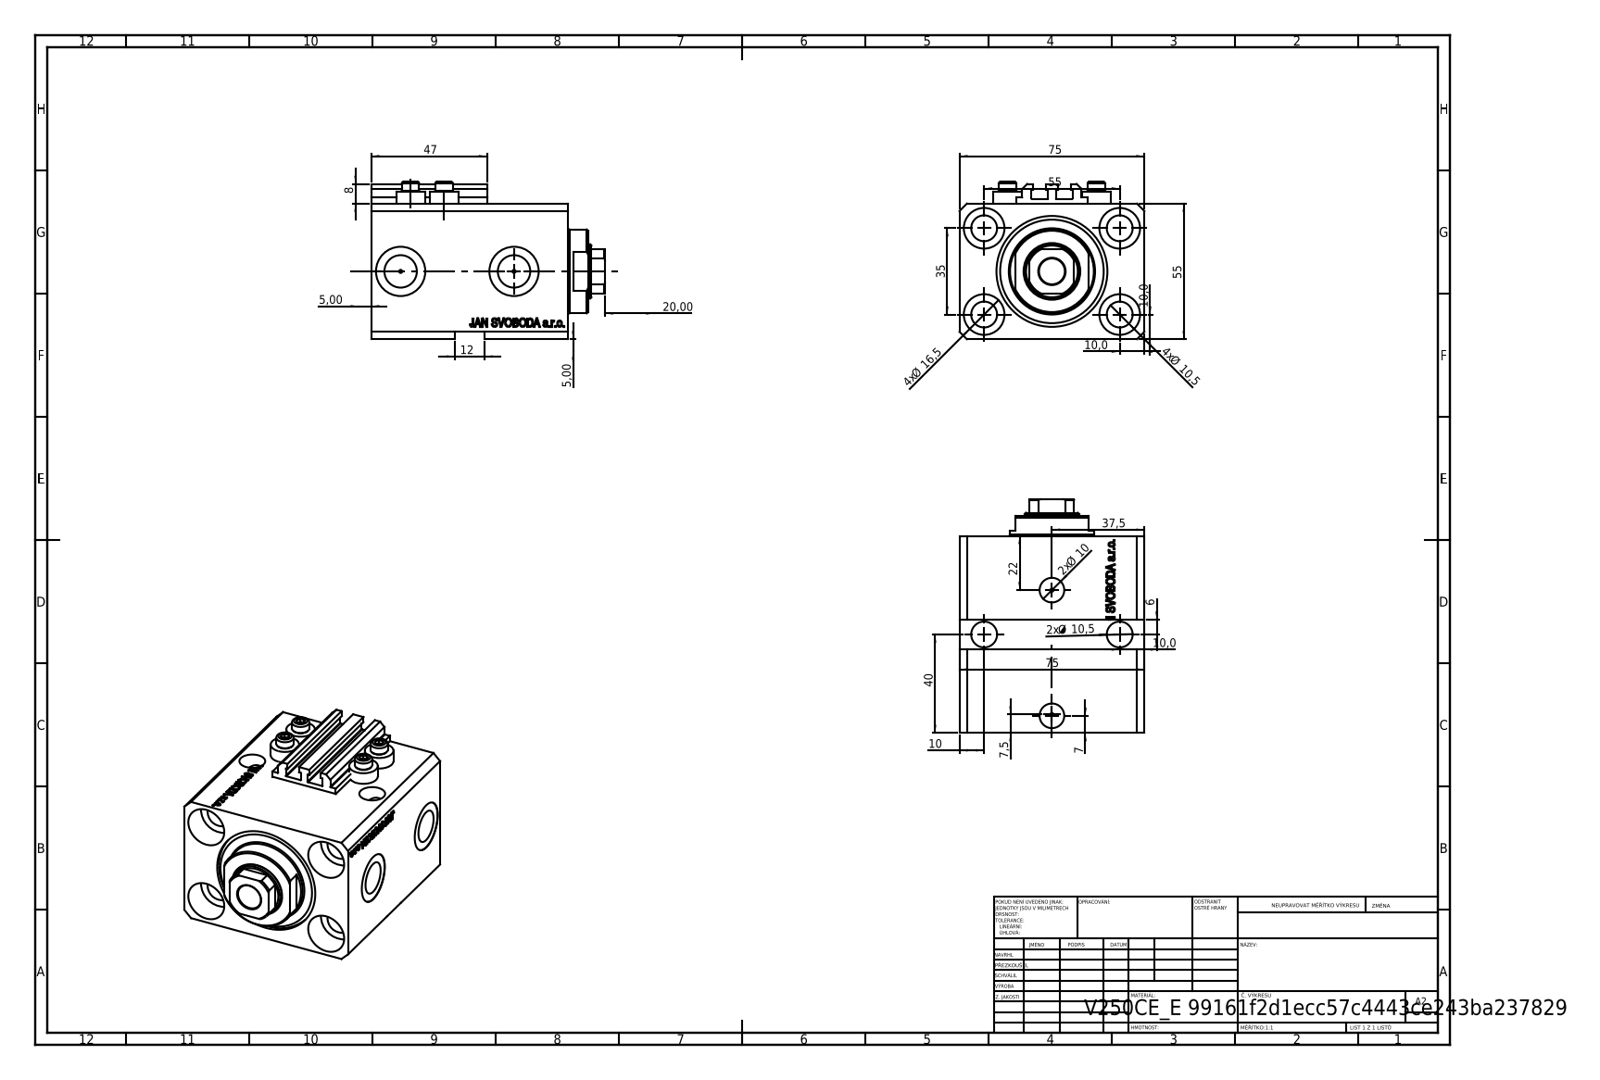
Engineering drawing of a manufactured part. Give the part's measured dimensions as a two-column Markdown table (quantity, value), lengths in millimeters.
| quantity | value |
| --- | --- |
| part name | V250CE_C_VCP; V250CE_E_Body; V250CE_VC_E; ALLEN BOLT V250CE |
| STEP written by | SolidWorks 2019 (CONFIG_CONTROL_DESIGN) |
| units | millimeters |
| bodies | 8 solids, 1080 faces (518 planar, 138 cylindrical, 424 other) |
| overall size | 94.9 × 75 × 64 |
| volume | 280 260 mm³ |
| surface area | 78 189 mm² |
| round holes (diameter × count) | 10.5 × 7, 1.25 × 4, 4 × 4, 16.5 × 4, 10 × 2, 13.16 × 2, 20 × 2, 22 × 1, 32 × 1, 45 × 1 |
| round bosses / shafts (diameter × count) | 11.6 × 4, 7 × 4, 34 × 1 |
| partial cylindrical surfaces (radius × count) | 0.2 × 10, 10.5 × 1 |
| main face-to-face distances | 55, 75, 80, 52.9, 27.1, 3, 9.9, 43, 70.1, 23 |
| hole center spacings | 32.6, 55, 13.6, 14.09, 19.89, 20.12, 25.81, 28.48 |
